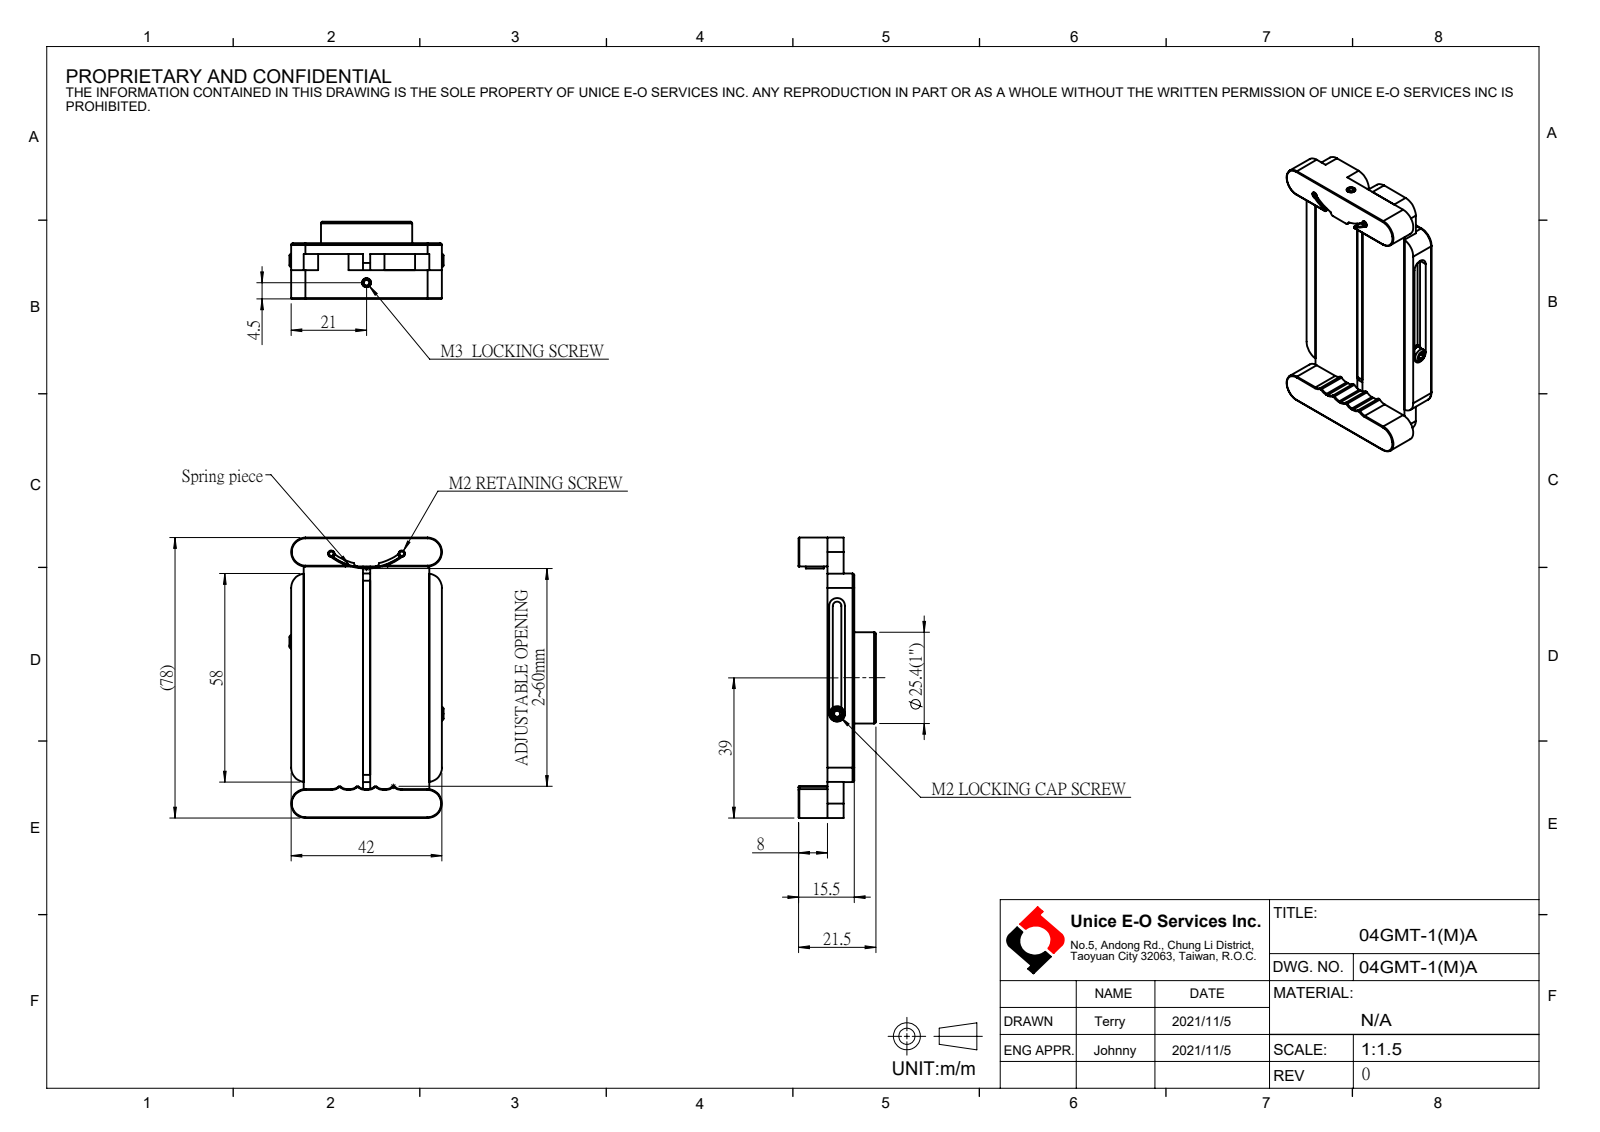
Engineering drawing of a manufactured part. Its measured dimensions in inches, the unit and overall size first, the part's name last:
Units: inches
Overall size (bounding box): 3.071 × 1.688 × 0.846
Round holes (diameter × count): ⌀0.098 ×1
Round bosses / shafts (diameter × count): ⌀0.165 ×2, ⌀0.146 ×2, ⌀0.079 ×2, ⌀1 ×1
Partial cylindrical surfaces — rounded edges, fillets, slot ends (radius × count): R0.157 ×16, R0.02 ×8, R0.118 ×8, R0.008 ×4, R0.087 ×4, R0.012 ×2, R0.031 ×2, R0.039 ×2
Main face-to-face distances: 0.177, 0.118, 0.295, 0.315, 0.65, 0.728, 0.61, 0.492, 0.236, 0.079
Bodies: 0 solids, 215 faces (83 planar, 84 cylindrical, 48 other)
Part name (STEP PRODUCT): 04GMT-1(M)A
STEP written by: SolidWorks 2021 (CONFIG_CONTROL_DESIGN)
